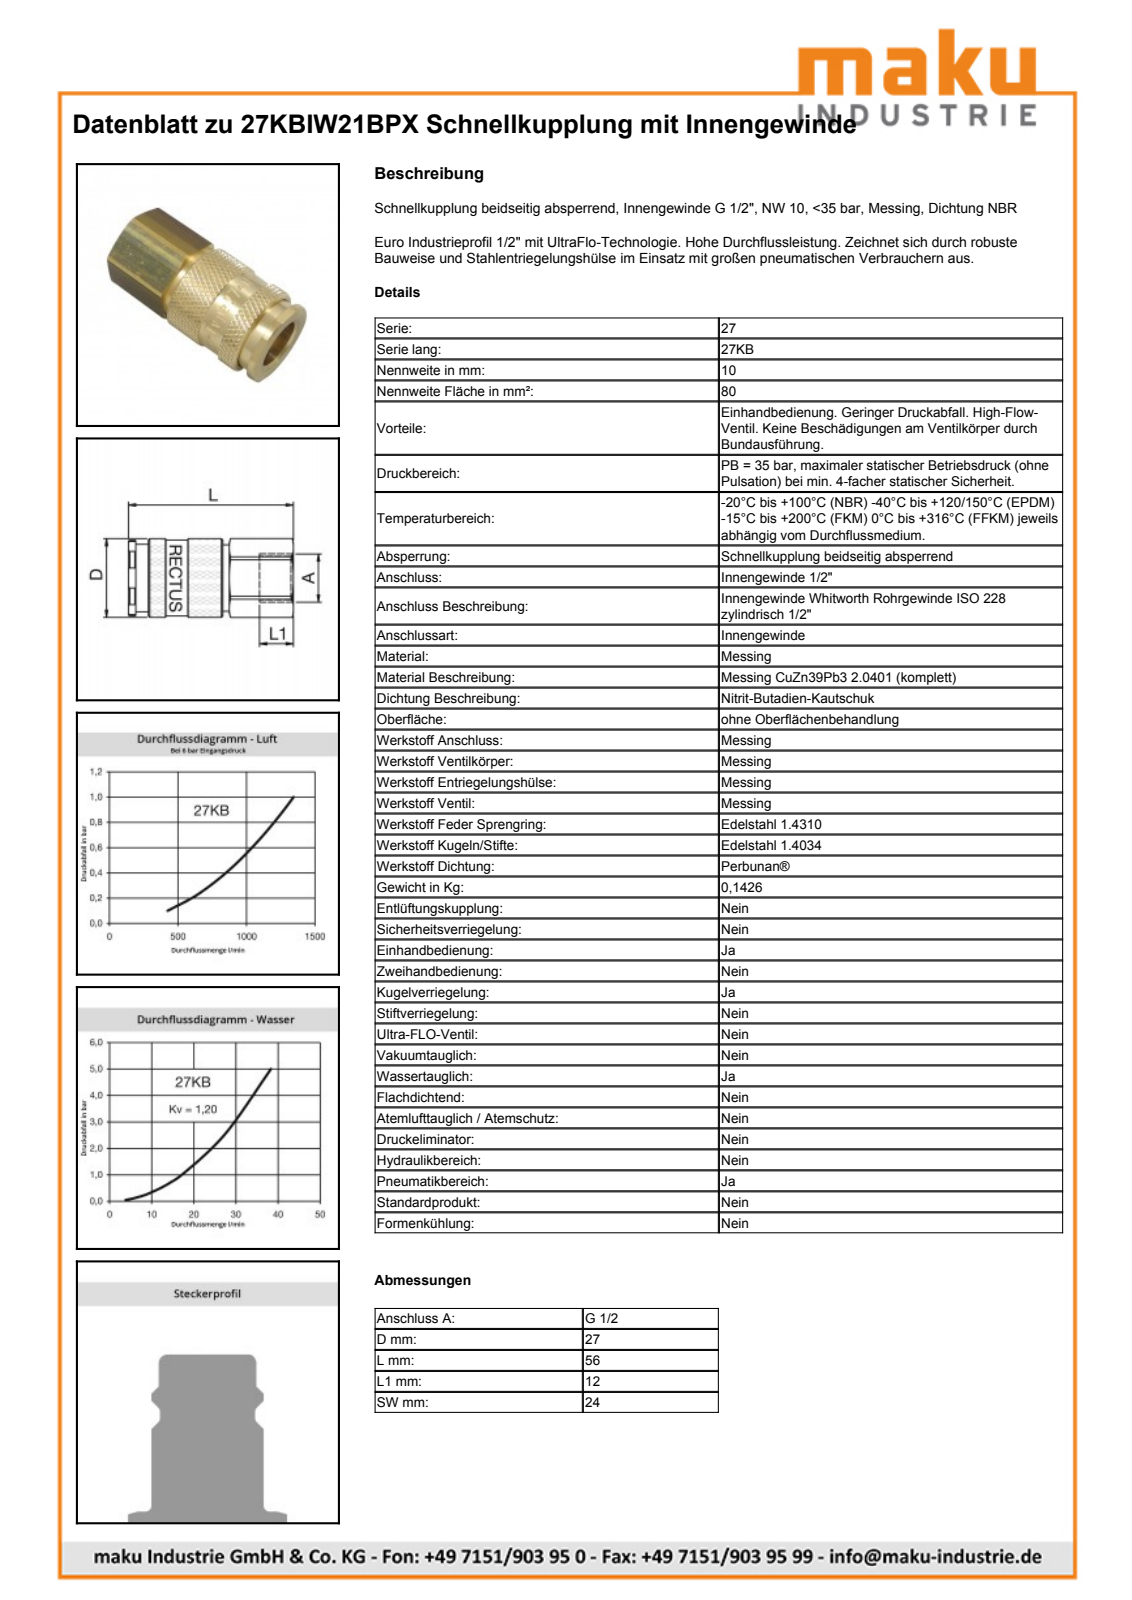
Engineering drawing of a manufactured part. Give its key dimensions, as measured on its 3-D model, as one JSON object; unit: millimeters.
{"part_name": "D106729", "step_written_by": "Autodesk Inventor 2011 (AUTOMOTIVE_DESIGN)", "units": "millimeters", "bodies": {"solids": 2, "faces": 652, "planar": 226, "cylindrical": 80, "other": 346}, "overall_size": [56.45, 27.15, 27.15], "volume_mm3": 23982, "surface_area_mm2": 10610, "round_holes": [[18, 1], [18.63, 1], [20.95, 1], [23.35, 1], [23.55, 1]], "round_bosses_or_shafts": [[27.15, 1], [26, 1], [23.1, 1], [22.75, 1], [20, 1]], "partial_cylinders_radius": [[9.68, 1], [9.9, 1], [12.9, 1], [13.53, 1]], "face_to_face_distances": [24, 24.02, 44.42, 32.3, 12.12, 56.45, 24.15, 12.03, 6.8, 25.5]}
